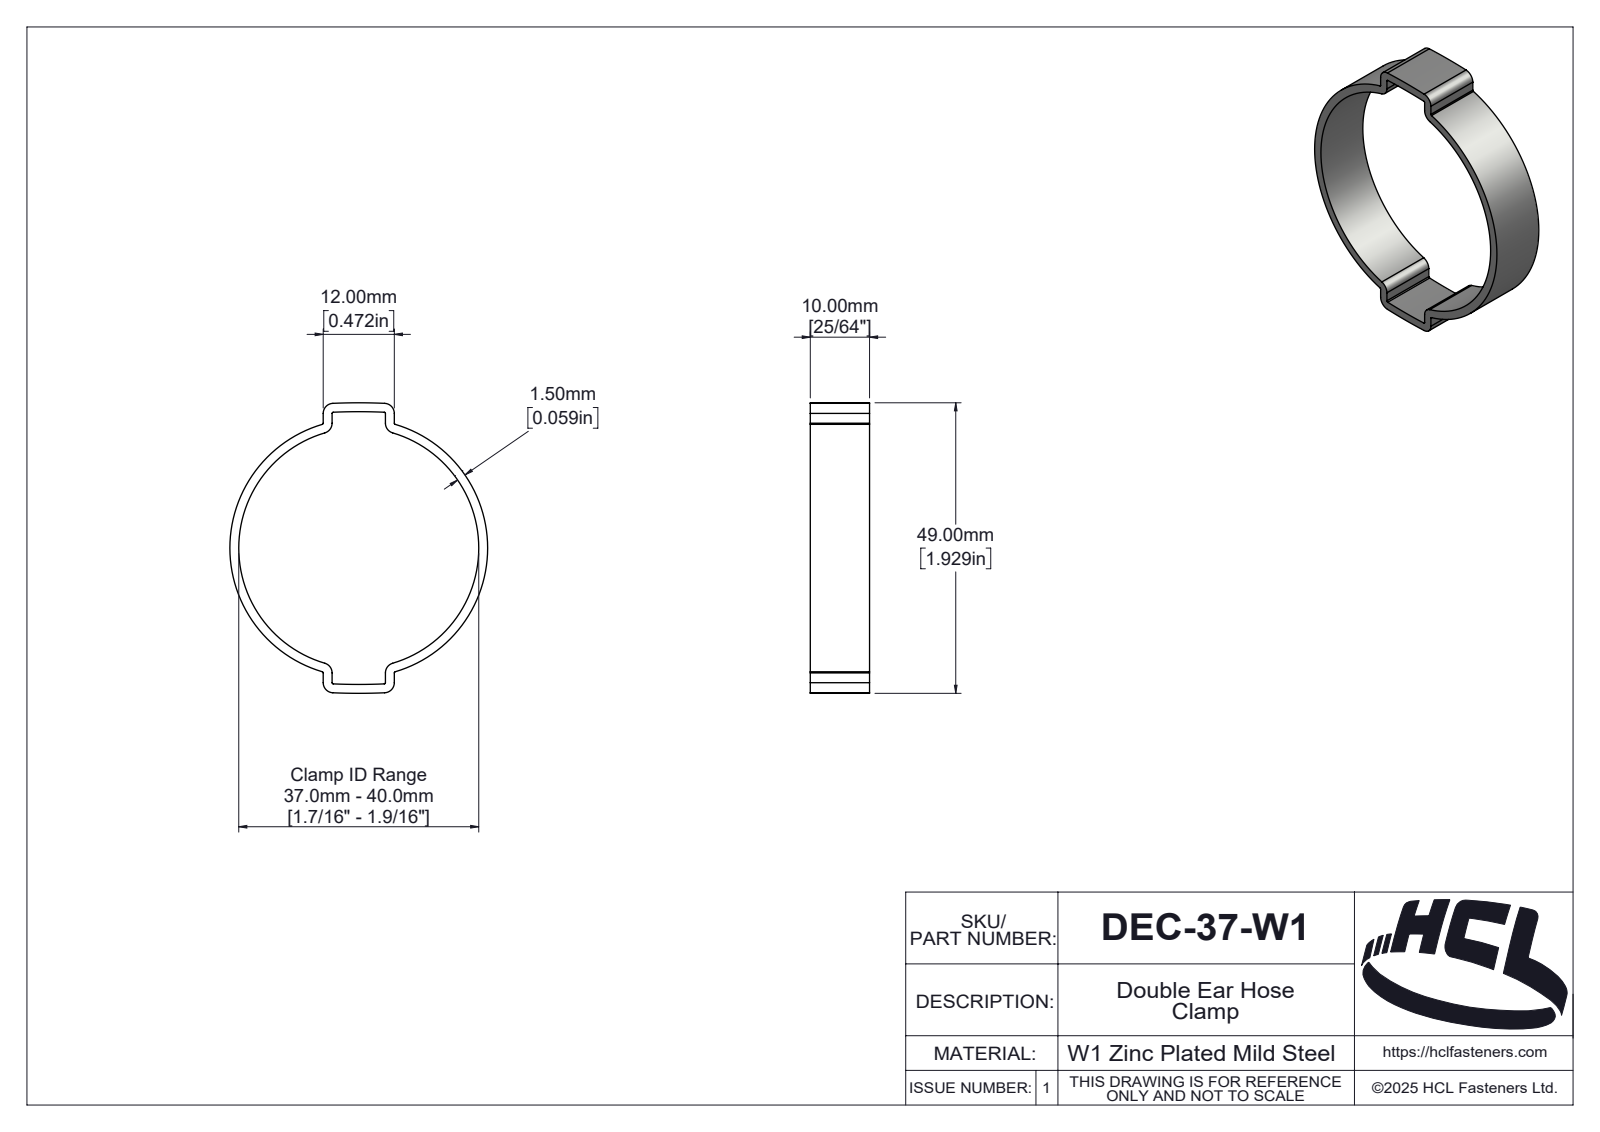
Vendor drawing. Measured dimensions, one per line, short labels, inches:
name: DEC-37-W1
written by: SolidWorks 2025 (AUTOMOTIVE_DESIGN)
unit: in
bodies: 1 solid, 137 faces (12 planar, 67 cylindrical, 58 other)
size: 1.929 × 1.713 × 0.394
volume: 0.13 in³; area: 5.09 in²
holes: 1× ⌀1.594
bosses: 1× ⌀1.713
rounds: 8× R0.008, 8× R0.067, 2× R3.988, 2× R4.047, 1× R0.011, 1× R0.044, 1× R0.056, 1× R0.059
face distances: 0.394, 0.059, 0.413, 0.472, 0.354, 0.23, 0.171, 0.183, 0.243, 0.222
